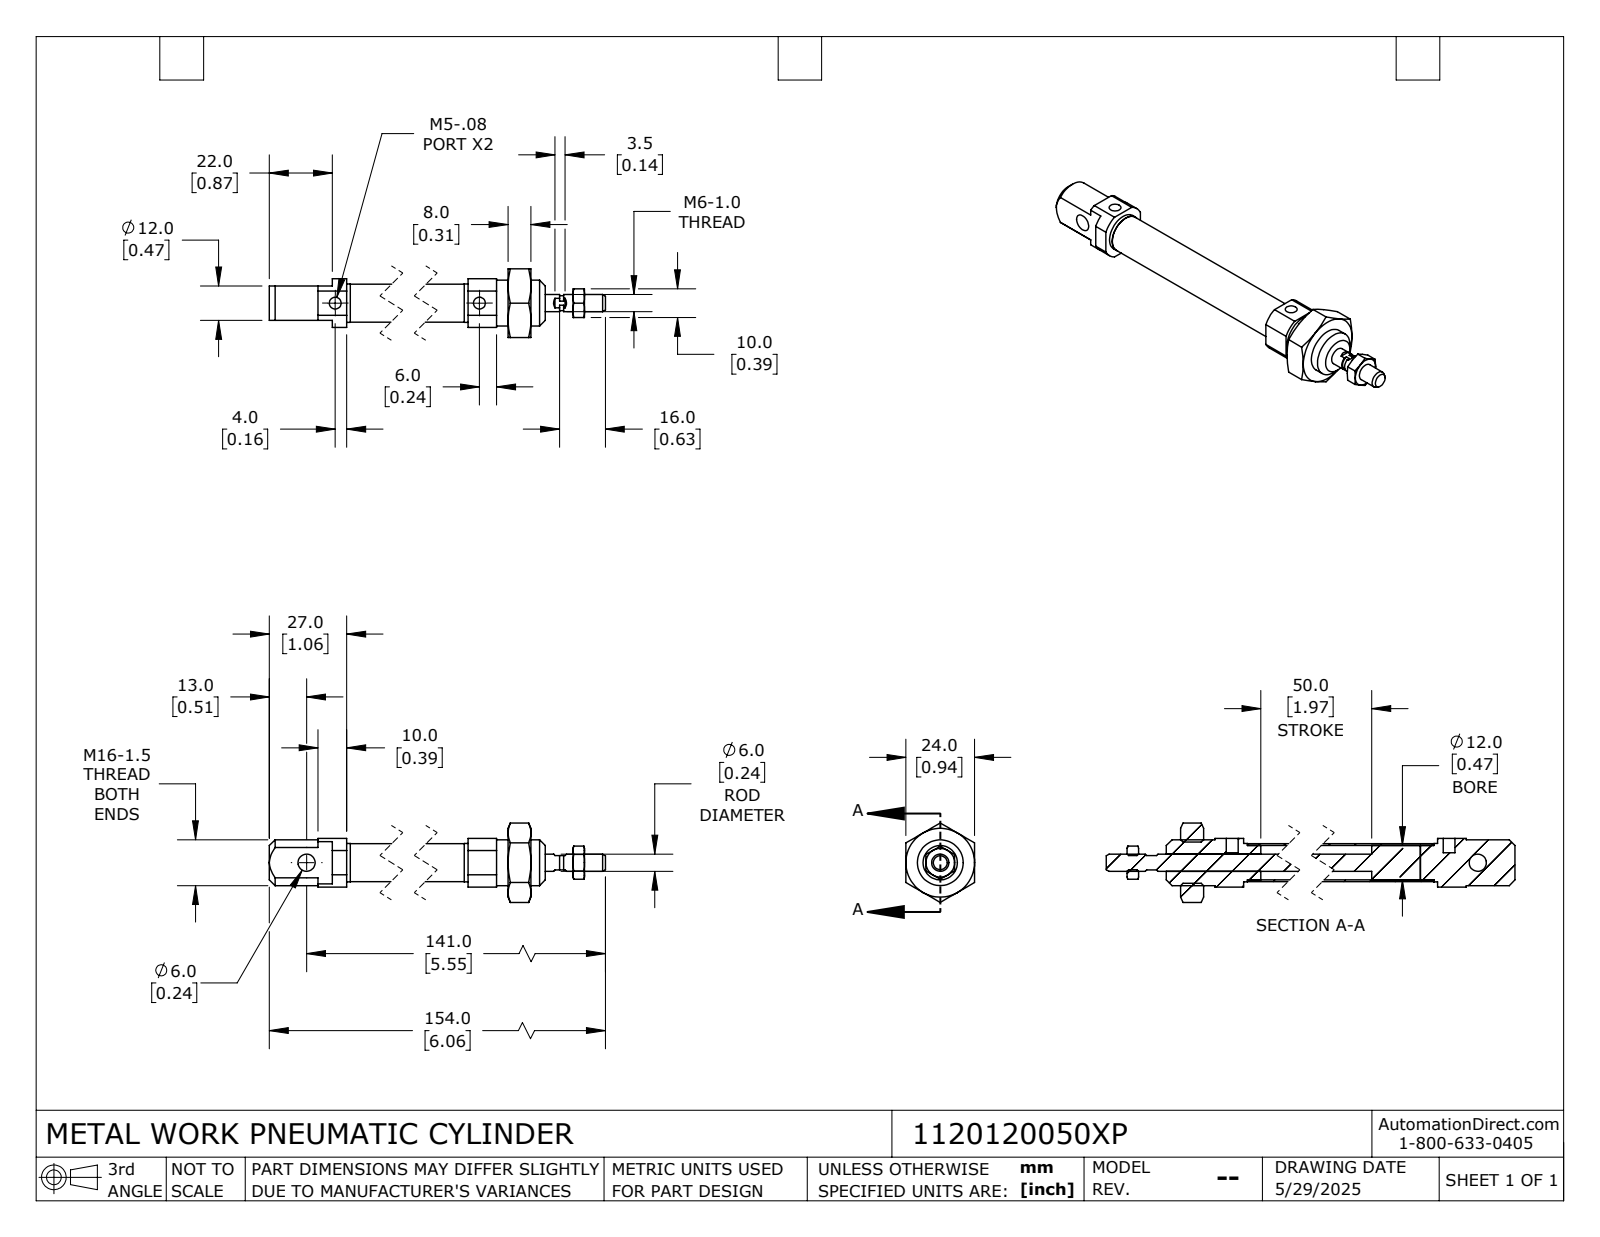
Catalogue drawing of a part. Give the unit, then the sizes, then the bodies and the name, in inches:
Units: inches
Overall size (bounding box): 6.063 × 1.091 × 0.945
Round holes (diameter × count): ⌀0.163 ×2, ⌀0.194 ×1, ⌀0.236 ×1, ⌀0.566 ×1
Round bosses / shafts (diameter × count): ⌀0.63 ×1, ⌀0.528 ×1, ⌀0.522 ×1, ⌀0.472 ×1, ⌀0.236 ×1, ⌀0.205 ×1
Partial cylindrical surfaces — rounded edges, fillets, slot ends (radius × count): R0.374 ×1
Main face-to-face distances: 0.669, 0.236, 0.945, 0.472, 4.173, 0.098, 0.571, 0.315, 0.138, 1.299
Hole centre spacings: 3.425
Volume: 1.269 in³ · Surface area: 24.76 in²
Bodies: 6 solids, 139 faces (56 planar, 45 cylindrical, 38 other)
Part name (STEP PRODUCT): 1120120050XP; 1120120050XP_ROD; 1120120050XP_BODY
STEP written by: SolidWorks 2024 (CONFIG_CONTROL_DESIGN)
